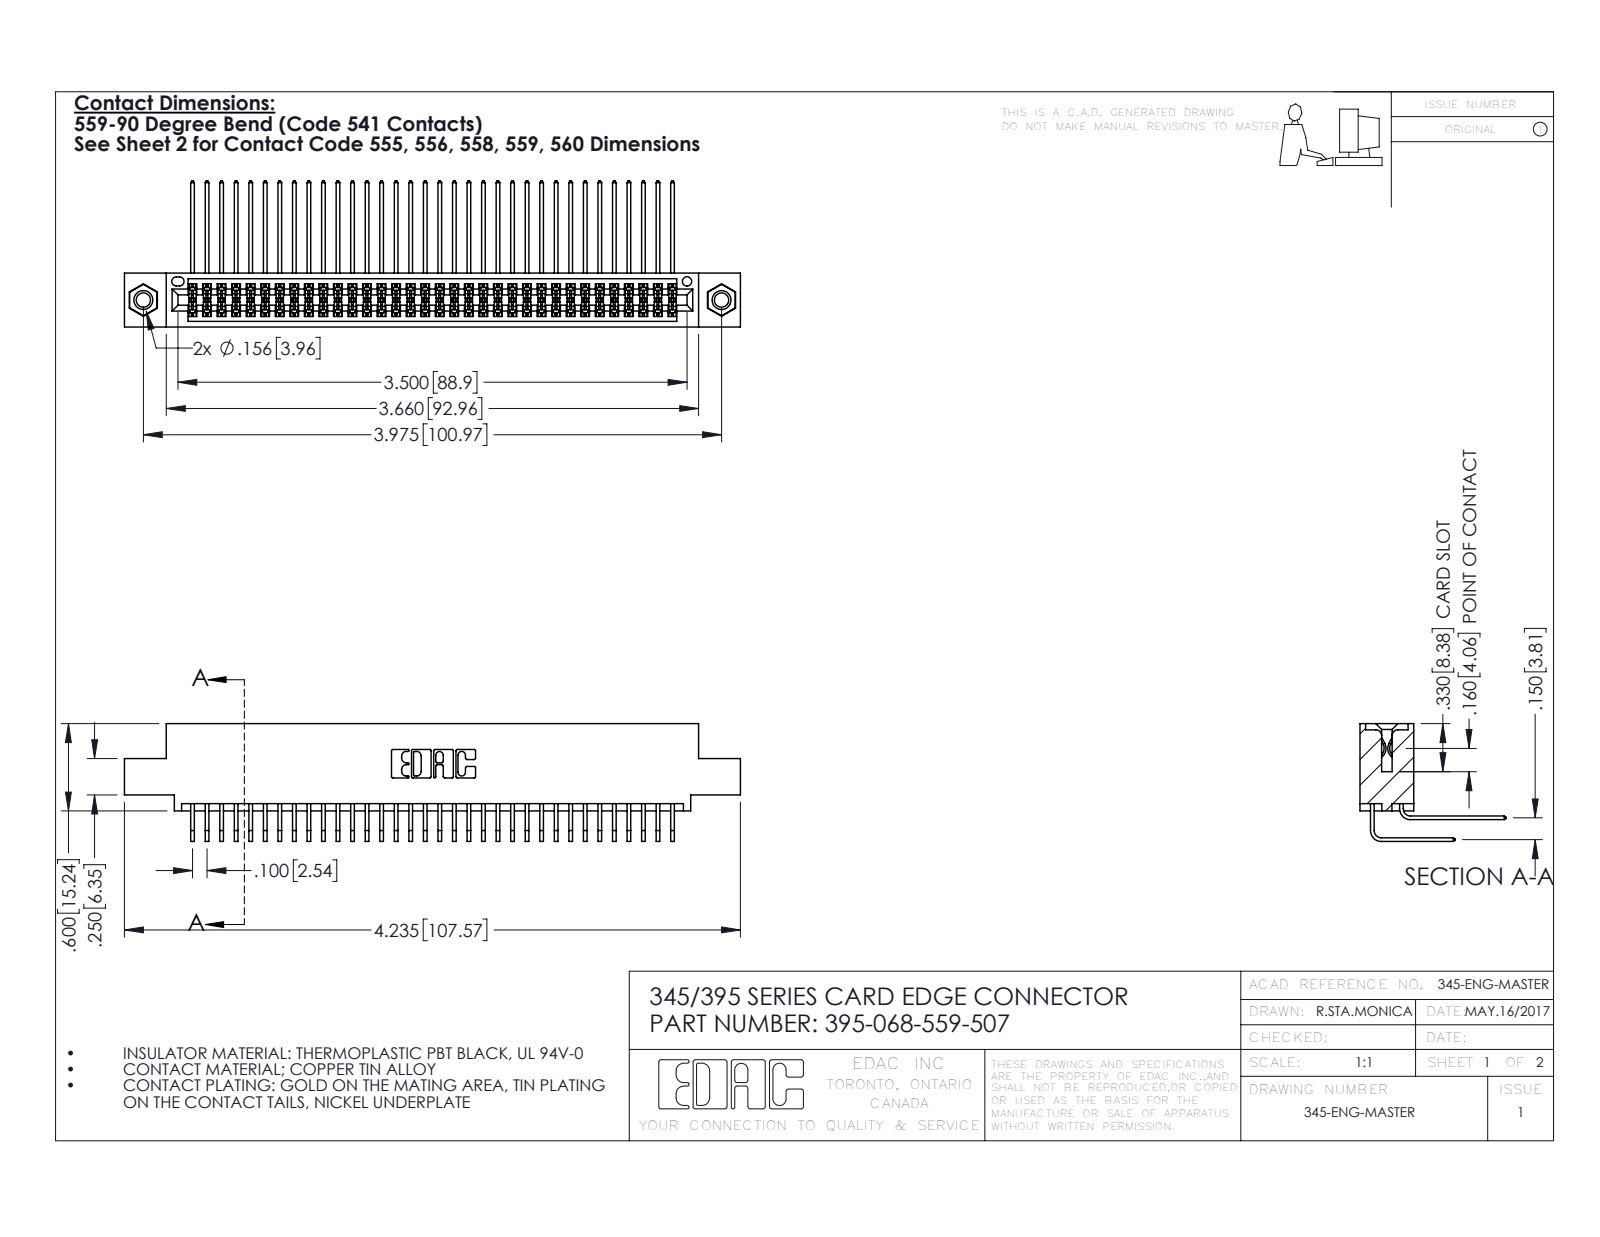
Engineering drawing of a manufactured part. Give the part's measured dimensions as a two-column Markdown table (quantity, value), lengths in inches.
| quantity | value |
| --- | --- |
| part name | 345-292-001_559 Tail - 2; 345-292-001_558 559 Tail - 1; 345-250-001_345-250-005-103; 345 Part_0.110 Offset - 0.156 Dia-TI (+1 more) |
| STEP written by | SolidWorks 2016 (CONFIG_CONTROL_DESIGN) |
| units | inches |
| bodies | 71 solids, 3726 faces (2496 planar, 1214 cylindrical, 16 other) |
| overall size | 4.235 × 1.005 × 0.809 |
| volume | 0.652 in³ |
| surface area | 27.28 in² |
| round holes (diameter × count) | 0.098 × 2, 0.125 × 2, 0.156 × 2, 0.064 × 1 |
| round bosses / shafts (diameter × count) | 0.155 × 2 |
| partial cylindrical surfaces (radius × count) | 0.006 × 103, 0.01 × 22, 0.007 × 6, 0.031 × 6, 0.026 × 3, 0.014 × 2, 0.019 × 2, 0.022 × 2 |
| main face-to-face distances | 0.072, 0.298, 0.2, 0.37, 0.098, 0.272, 0.025, 0.225, 0.175, 0.15 |
| hole center spacings | 0.27, 3.74, 3.975 |
